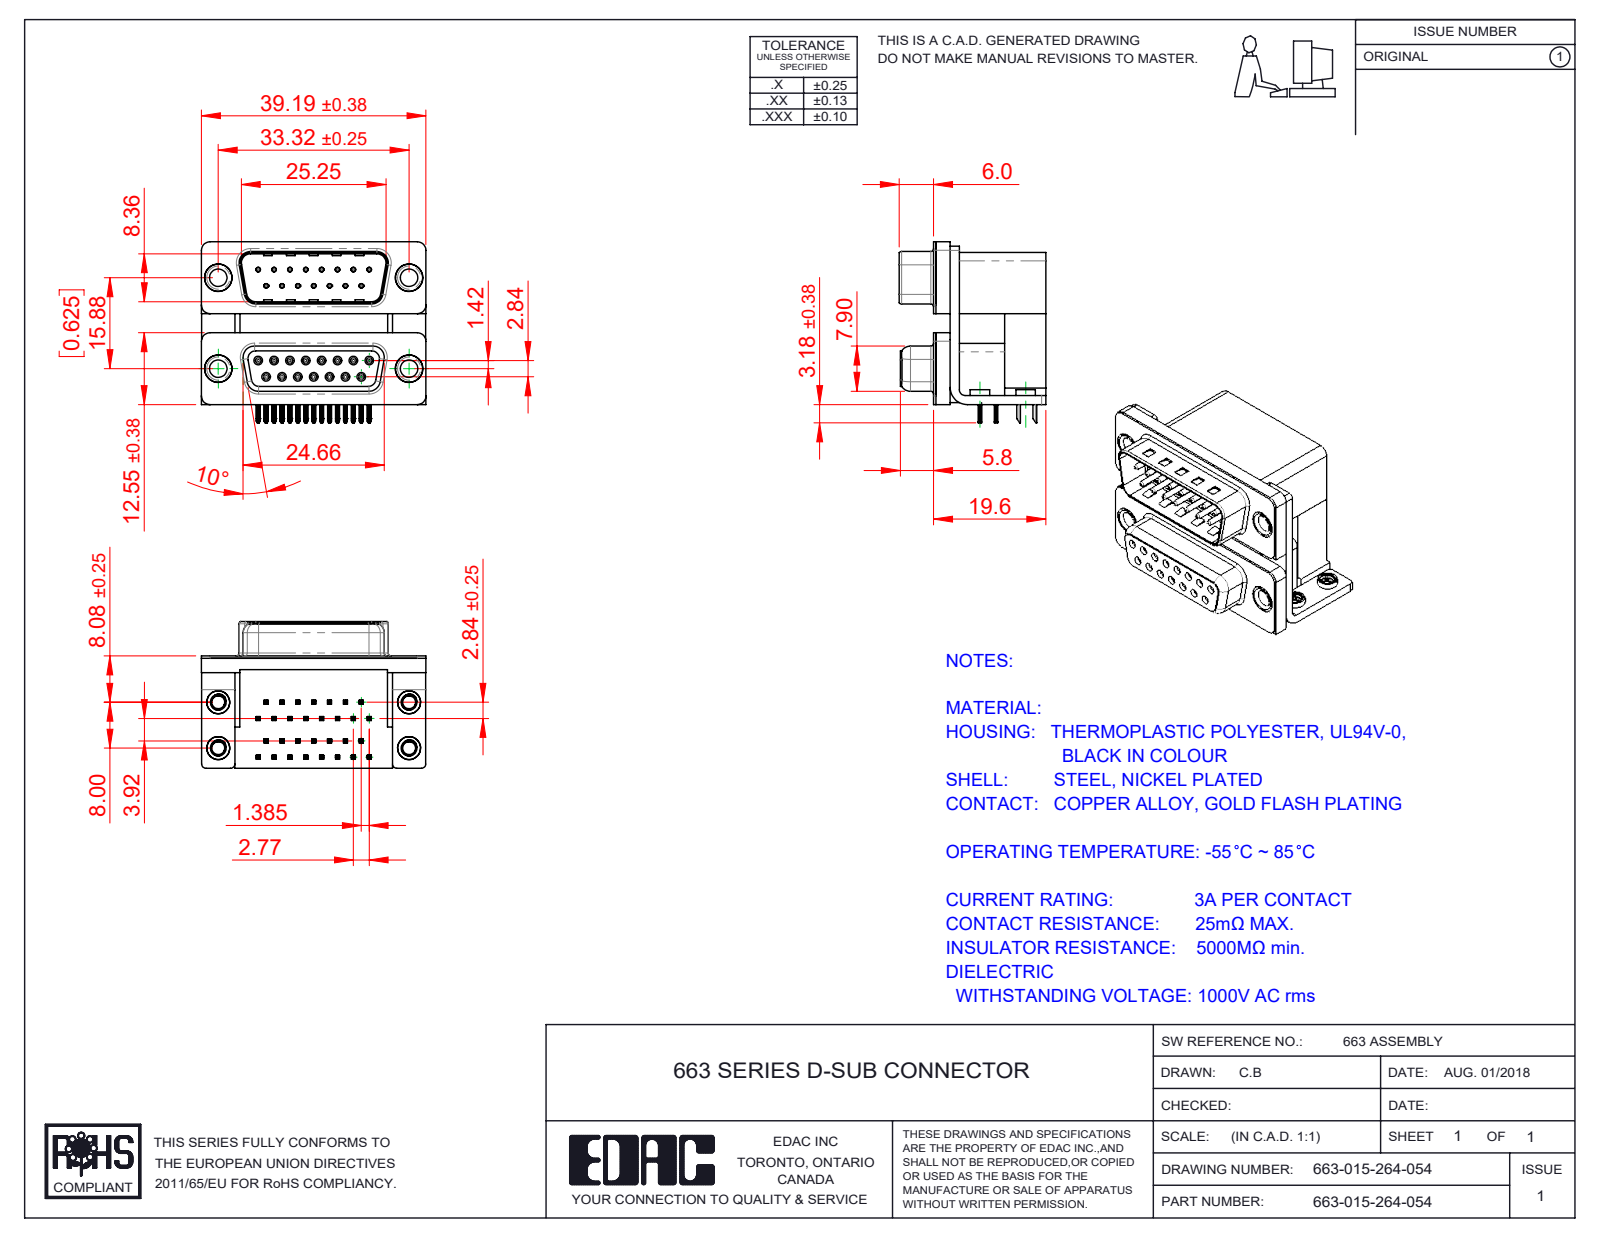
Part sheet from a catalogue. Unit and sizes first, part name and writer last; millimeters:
Units: millimetres
Overall size (bounding box): 39.19 × 31.61 × 25.6
Round holes (diameter × count): ⌀0.8 ×30, ⌀0.35 ×15, ⌀0.9 ×15, ⌀2.26 ×4, ⌀2.75 ×4, ⌀3.05 ×4, ⌀3.2 ×4, ⌀3.5 ×4, ⌀4 ×4, ⌀4.8 ×4, ⌀5 ×4
Round bosses / shafts (diameter × count): ⌀1.2 ×15, ⌀0.75 ×15, ⌀4.9 ×4, ⌀4.75 ×4, ⌀4 ×4, ⌀3.85 ×4, ⌀3.4 ×4
Partial cylindrical surfaces — rounded edges, fillets, slot ends (radius × count): R0.1 ×120, R0.15 ×60, R0.25 ×60, R0.12 ×30, R0.35 ×30, R1.5 ×16, R0.34 ×15, R0.5 ×12
Main face-to-face distances: 0.4, 19.2, 16.7, 2.5, 10.7, 7.2, 12, 9.5, 2.9, 19.6
Hole centre spacings: 3.16, 16.12, 2.77, 16.82, 5.54, 8.31, 15.88, 17.92
Volume: 14 601 mm³ · Surface area: 16 364 mm²
Bodies: 45 solids, 3968 faces (2027 planar, 1054 cylindrical, 887 other)
Part name (STEP PRODUCT): 663 Contact Top Lower; 663 Housing Spacer_15 Contacts L; 663-015-264-054; 663 Contact Top Upper_L (+8 more)
STEP written by: SolidWorks 2020 (CONFIG_CONTROL_DESIGN)
